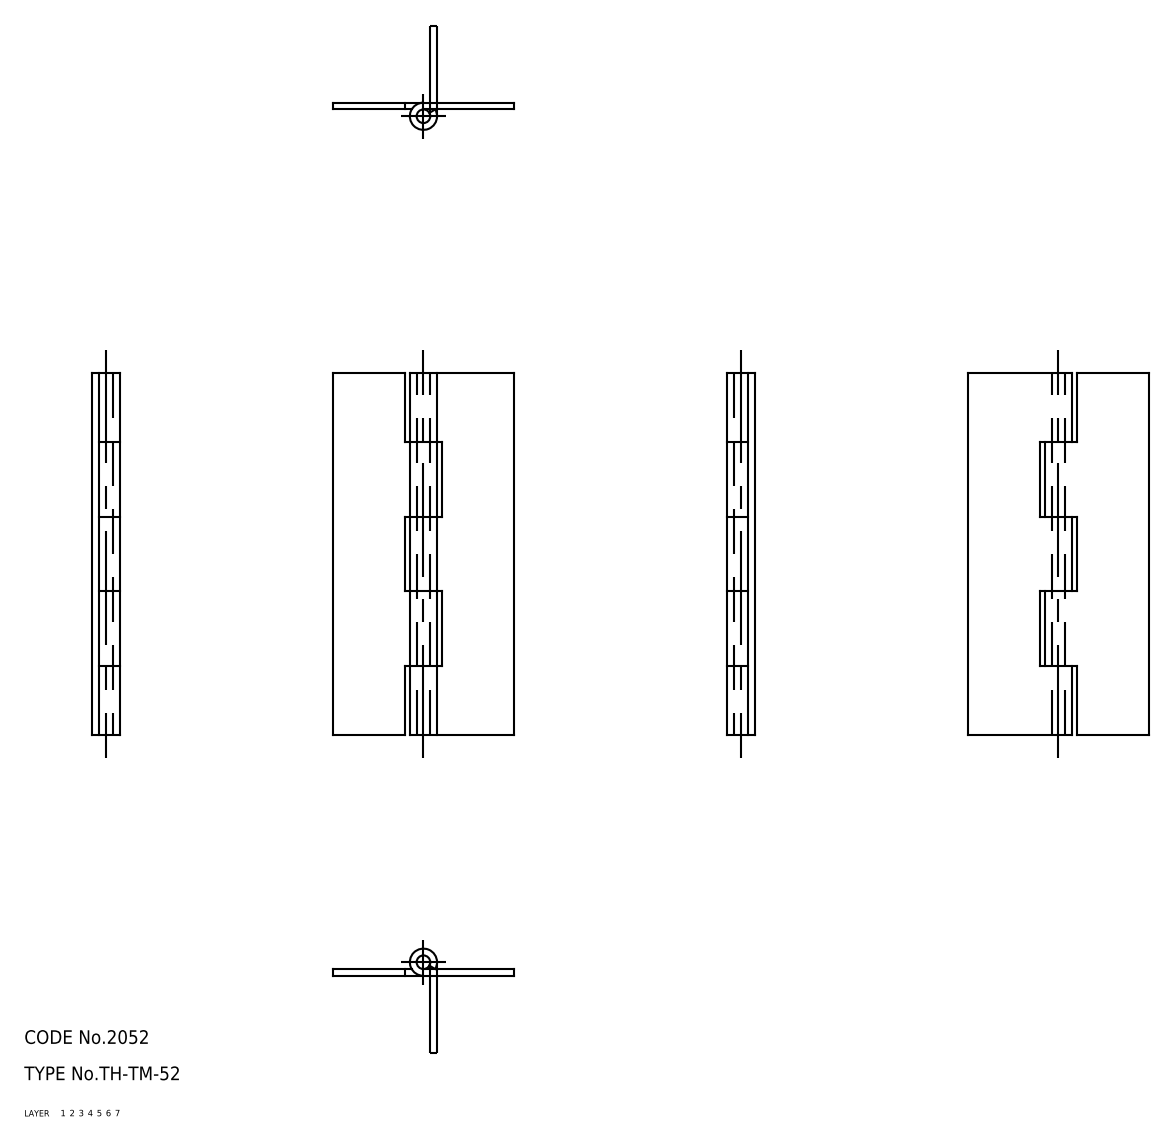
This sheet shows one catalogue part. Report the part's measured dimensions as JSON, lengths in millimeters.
{"part_name": "hinge piece_B; hinge piece_A; shaft; TH_TM_52_24002_36", "step_written_by": "CADfix (AUTOMOTIVE_DESIGN)", "units": "millimeters", "bodies": {"solids": 3, "faces": 42, "planar": 0, "cylindrical": 0, "other": 42}, "overall_size": [80, 40, 6], "volume_mm3": 6295, "surface_area_mm2": 9219}
